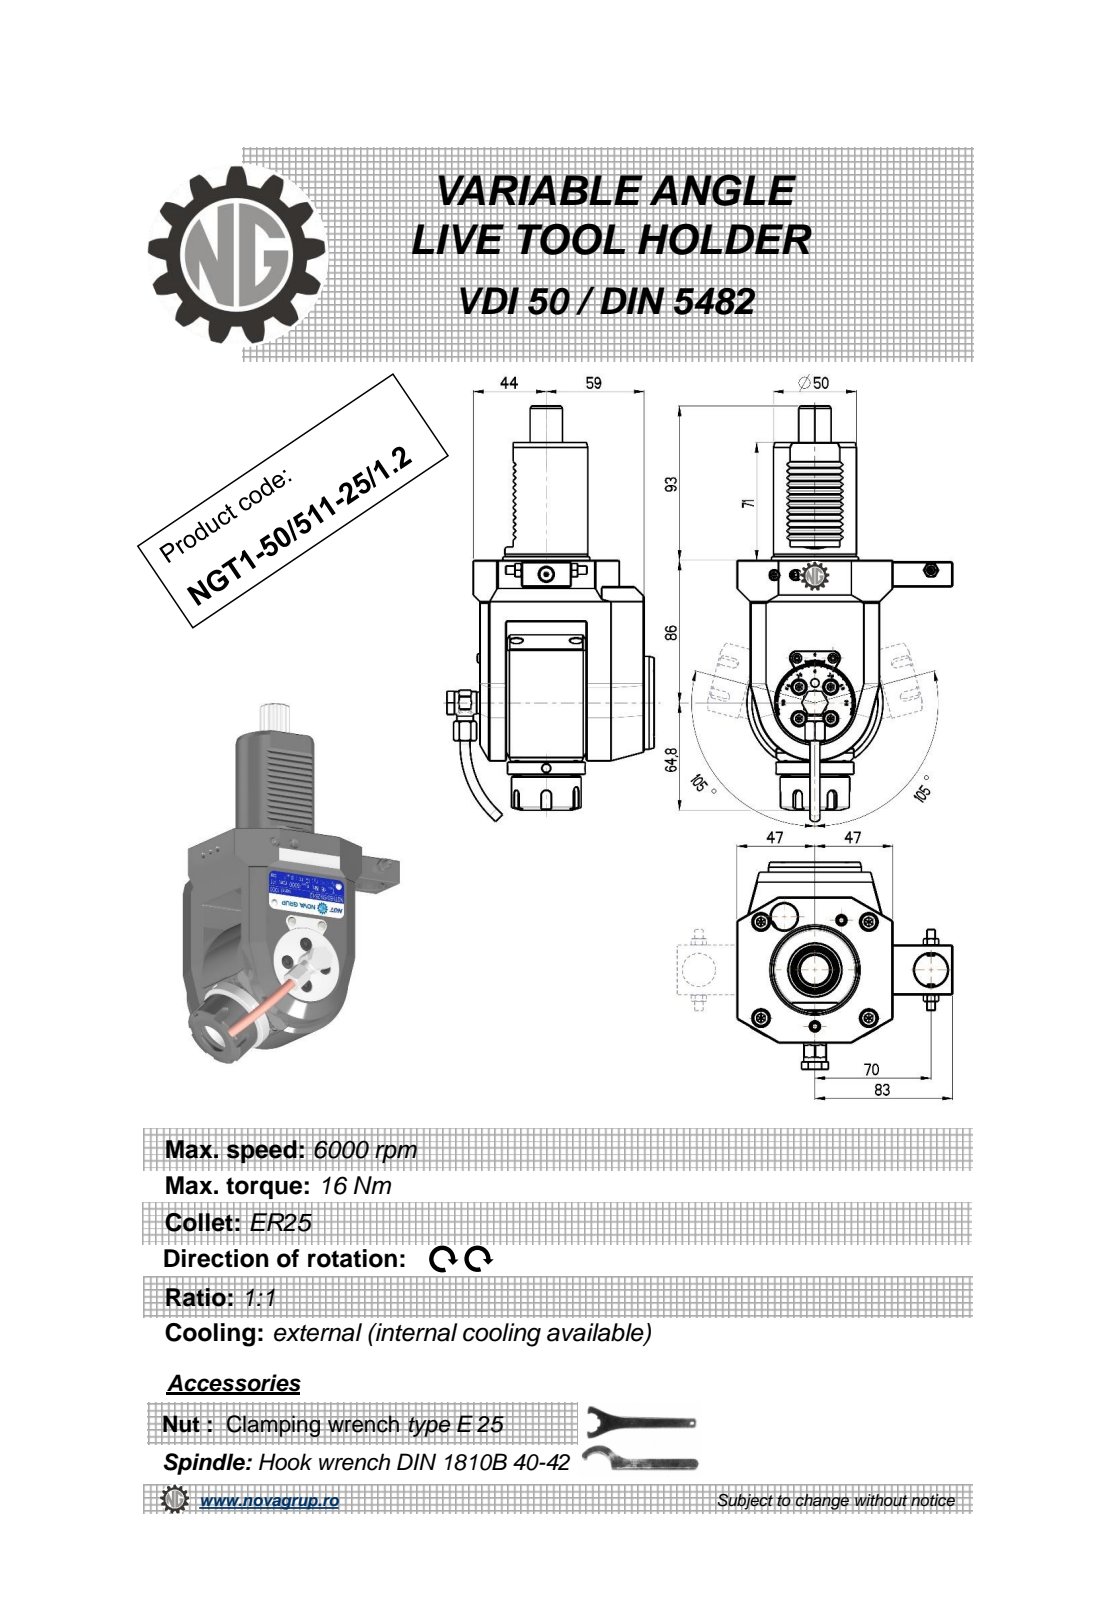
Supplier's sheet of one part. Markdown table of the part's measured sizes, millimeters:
| quantity | value |
| --- | --- |
| part name | NGT1_50_511_25_1_2 |
| STEP written by | PRO/ENGINEER BY PARAMETRIC TECHNOLOGY CORPORATION, 2010280 (CONFIG_CONTROL_DESIGN) |
| units | millimeters |
| bodies | 1 solid, 659 faces (261 planar, 184 cylindrical, 214 other) |
| overall size | 250.67 × 130 × 124.9 |
| volume | 1 013 000 mm³ |
| surface area | 91 578 mm² |
| round holes (diameter × count) | 4 × 3, 5 × 2, 3 × 1, 6.2 × 1, 9 × 1, 9.5 × 1, 10 × 1, 11 × 1, 20 × 1, 20.3 × 1 |
| round bosses / shafts (diameter × count) | 6 × 2, 5.7 × 2, 82 × 1, 56 × 1, 50 × 1, 47 × 1, 42 × 1, 35 × 1 |
| partial cylindrical surfaces (radius × count) | 3.33 × 24, 0.26 × 12, 0.3 × 12, 0.16 × 6, 3 × 5, 0.5 × 4, 1 × 2, 10 × 2 |
| main face-to-face distances | 37, 16, 99, 8, 6, 21, 64, 105, 20, 35 |
| hole center spacings | 0.4, 39.45, 49, 49.4, 70, 85.45, 85.68, 116.95 |
